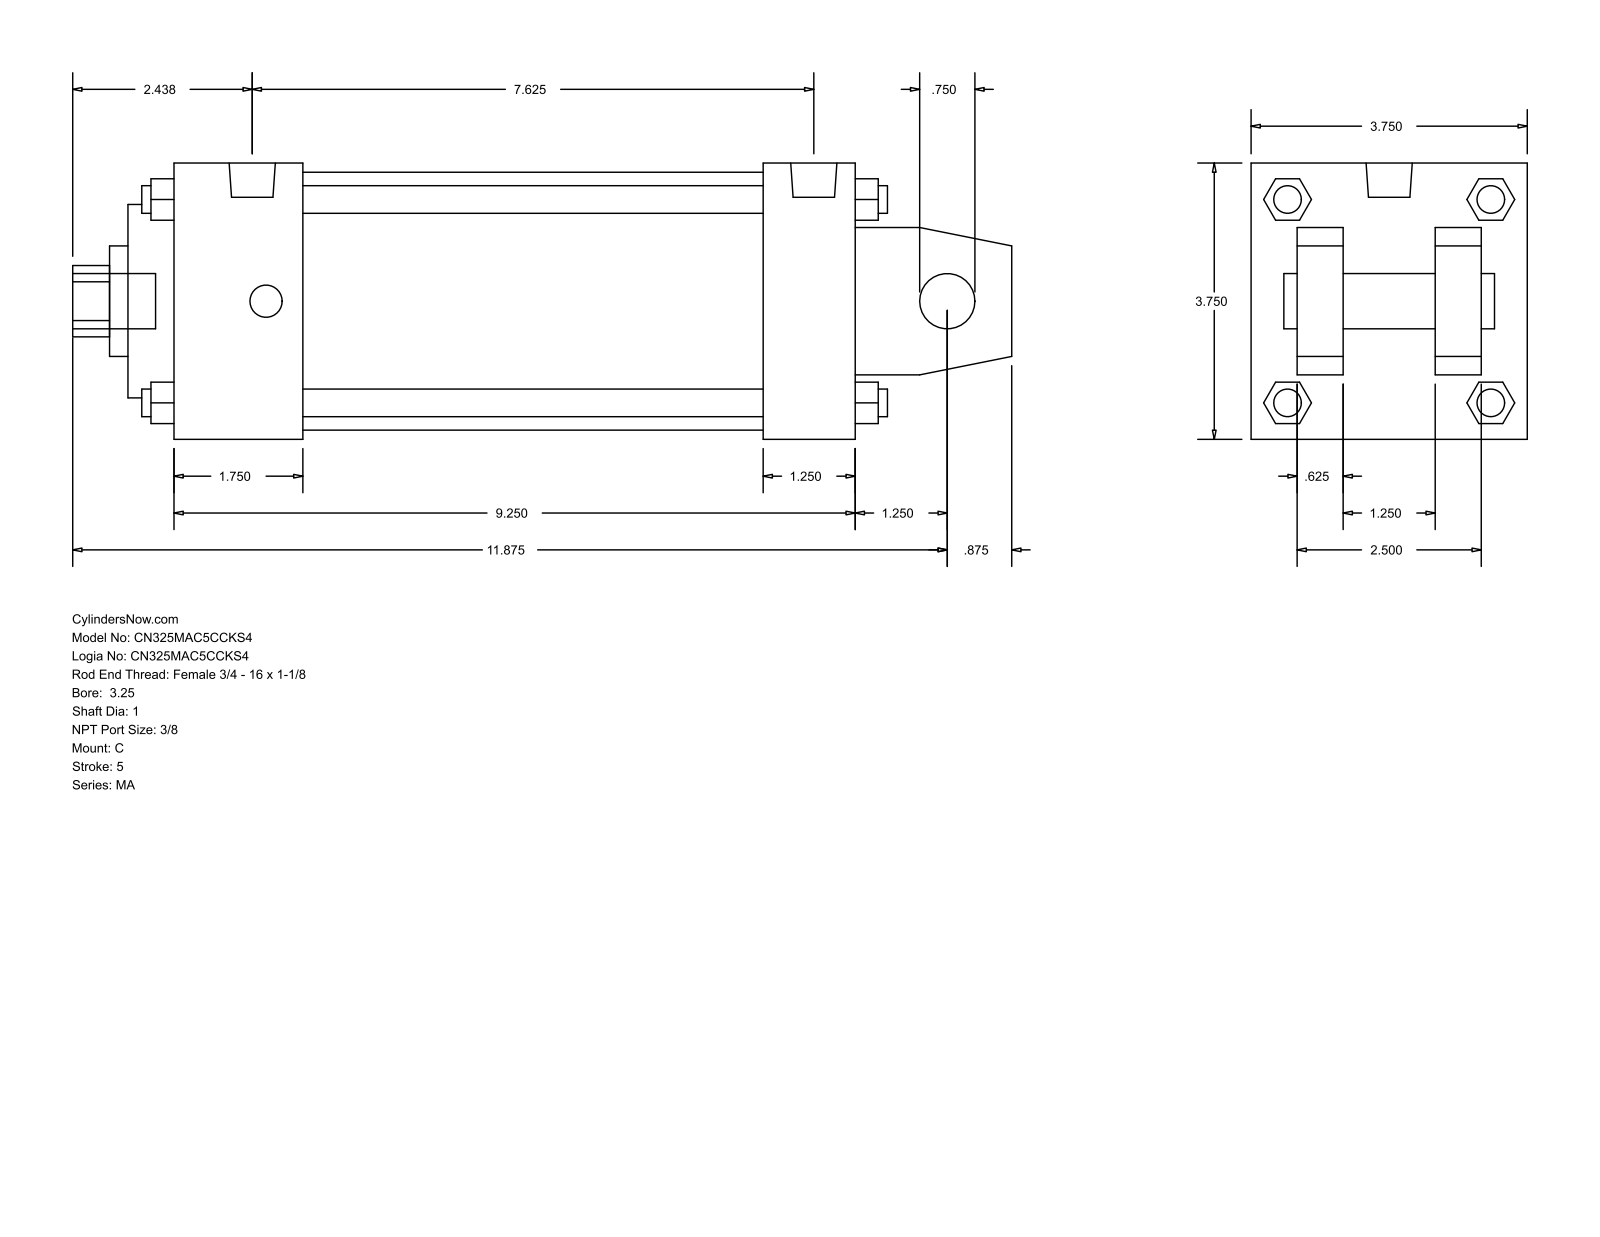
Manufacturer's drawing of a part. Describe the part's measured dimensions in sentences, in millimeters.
The part is named "MA_C__0325_1". Its 3-D file was written by "GSSL Pune (CONFIG_CONTROL_DESIGN)". It is 0 solids with 141 faces: 109 planar, 32 cylindrical and 0 other. Overall it measures 323.85 by 95.25 by 95.25 millimeters. Round holes: 1 of diameter 19.05, 1 of diameter 25.4, 1 of diameter 38.1, 1 of diameter 66.67, 1 of diameter 88.9. Round bosses or shafts: 4 of diameter 11.11, 4 of diameter 9.53, 2 of diameter 15.93, 1 of diameter 19.05. Partial cylindrical surfaces (rounded edges, fillets, slot ends): 1 of radius 12.29. The main face-to-face distances are 95.24, 15.87, 63.5, 234.96, 31.76, 31.74, 79.37, 47.63, 203.2, 44.46.
